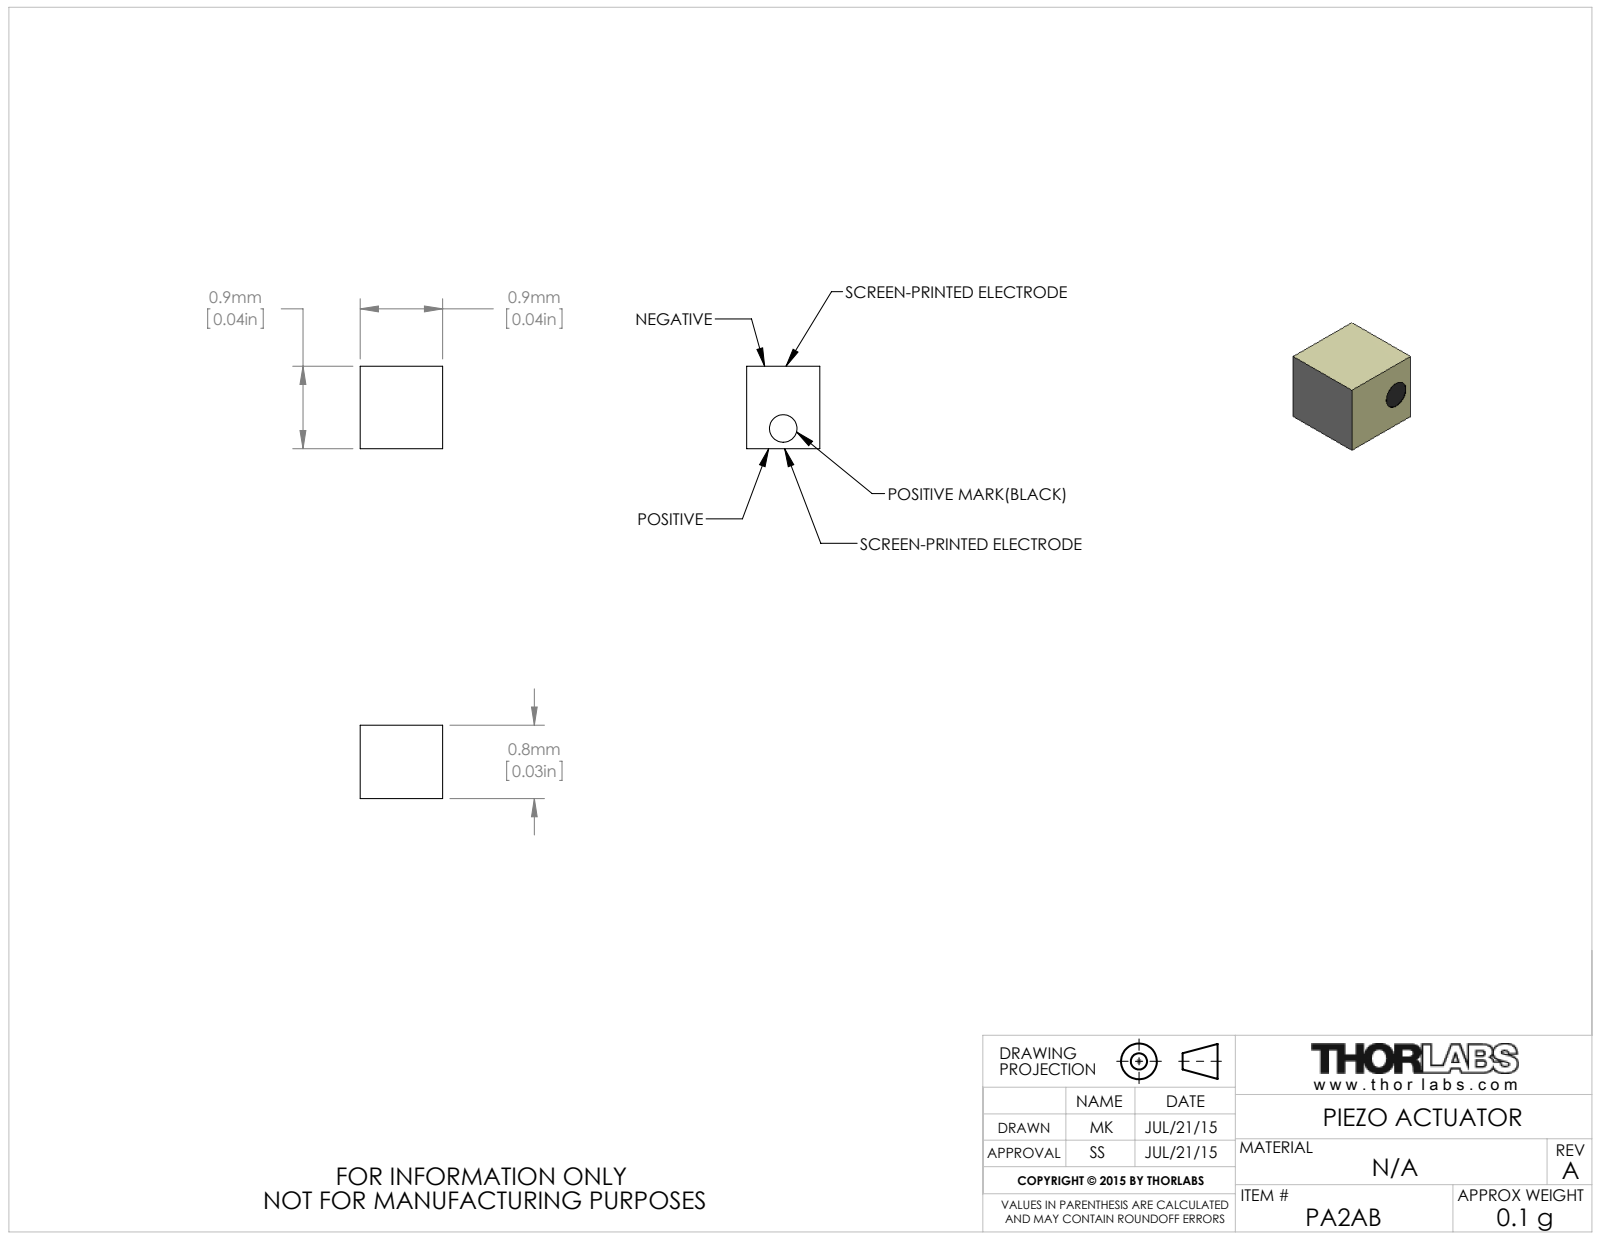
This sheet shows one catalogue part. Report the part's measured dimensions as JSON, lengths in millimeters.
{"part_name": "CTN003093", "step_written_by": "SolidWorks 2014 (AUTOMOTIVE_DESIGN)", "units": "millimeters", "bodies": {"solids": 1, "faces": 9, "planar": 7, "cylindrical": 2, "other": 0}, "overall_size": [0.9, 0.9, 0.8], "volume_mm3": 0.648, "surface_area_mm2": 4, "round_holes": [[0.3, 1]], "face_to_face_distances": [0.9, 0.8, 0.89]}
